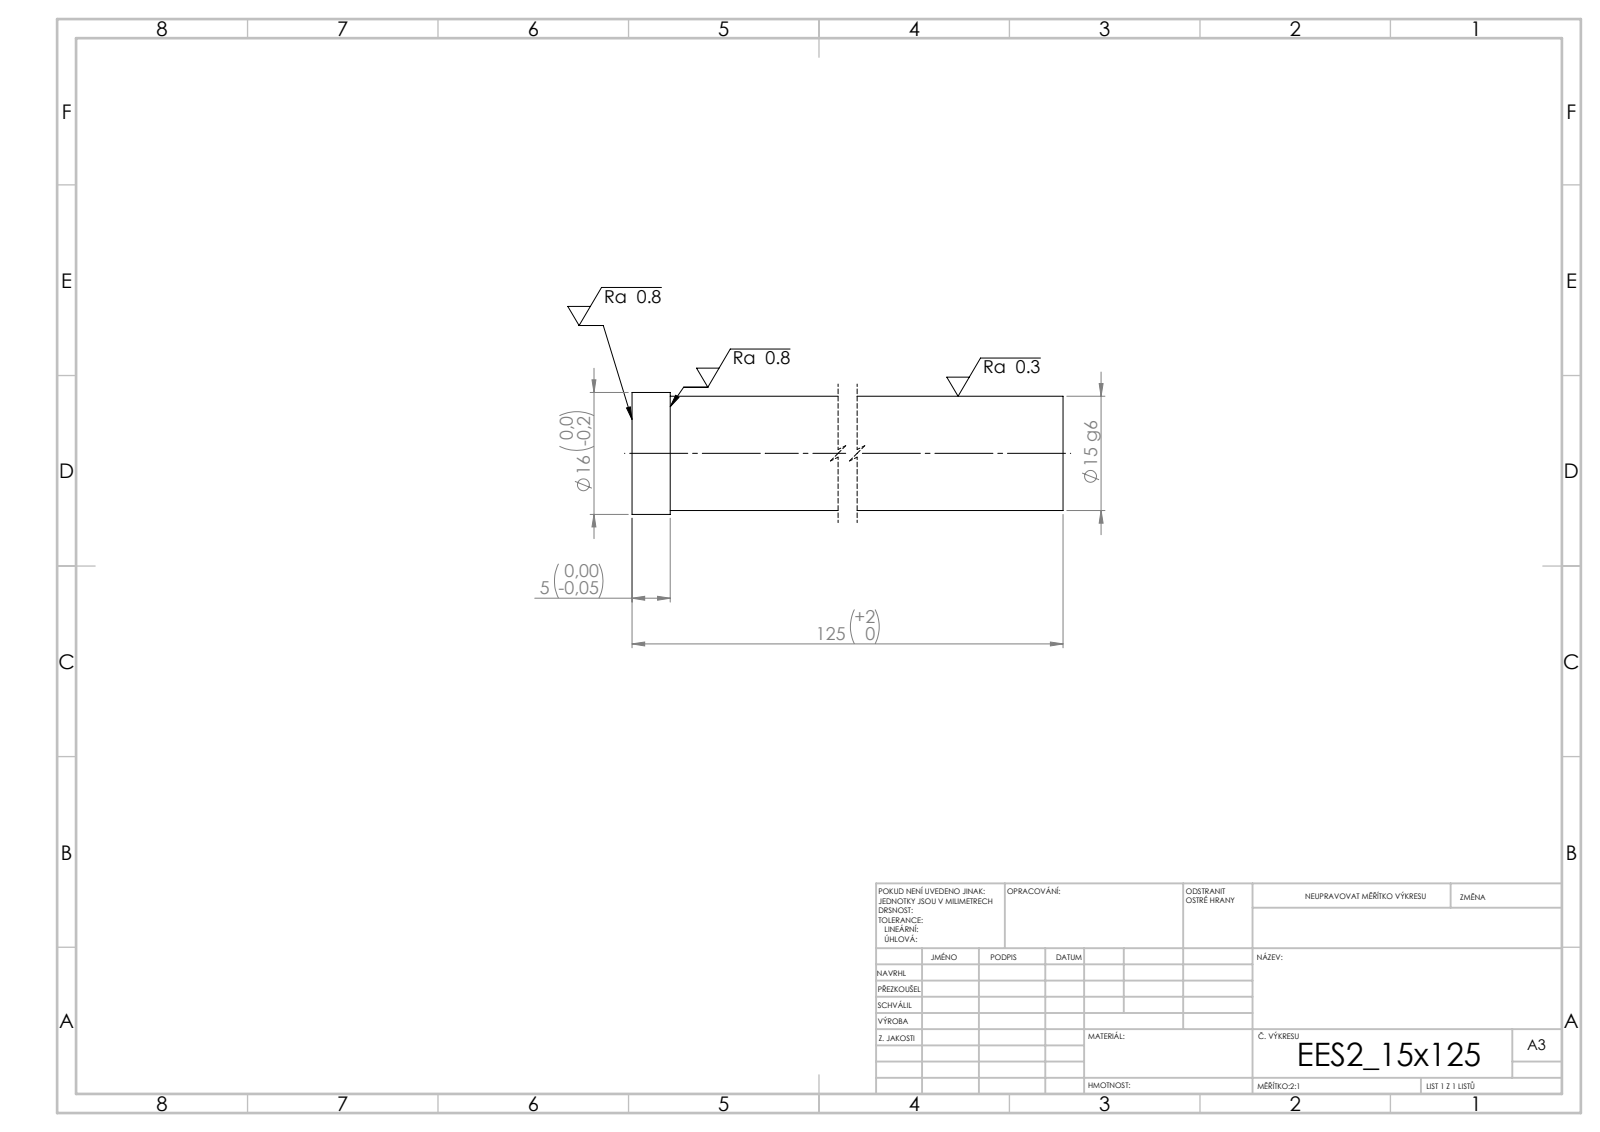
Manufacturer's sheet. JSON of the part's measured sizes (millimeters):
{"step_written_by": "SolidWorks 2019 (CONFIG_CONTROL_DESIGN)", "units": "millimeters", "bodies": {"solids": 1, "faces": 7, "planar": 3, "cylindrical": 4, "other": 0}, "overall_size": [125, 16, 16], "volume_mm3": 22211, "surface_area_mm2": 6308, "round_bosses_or_shafts": [[16, 1], [15, 1]], "face_to_face_distances": [125, 5, 120]}
